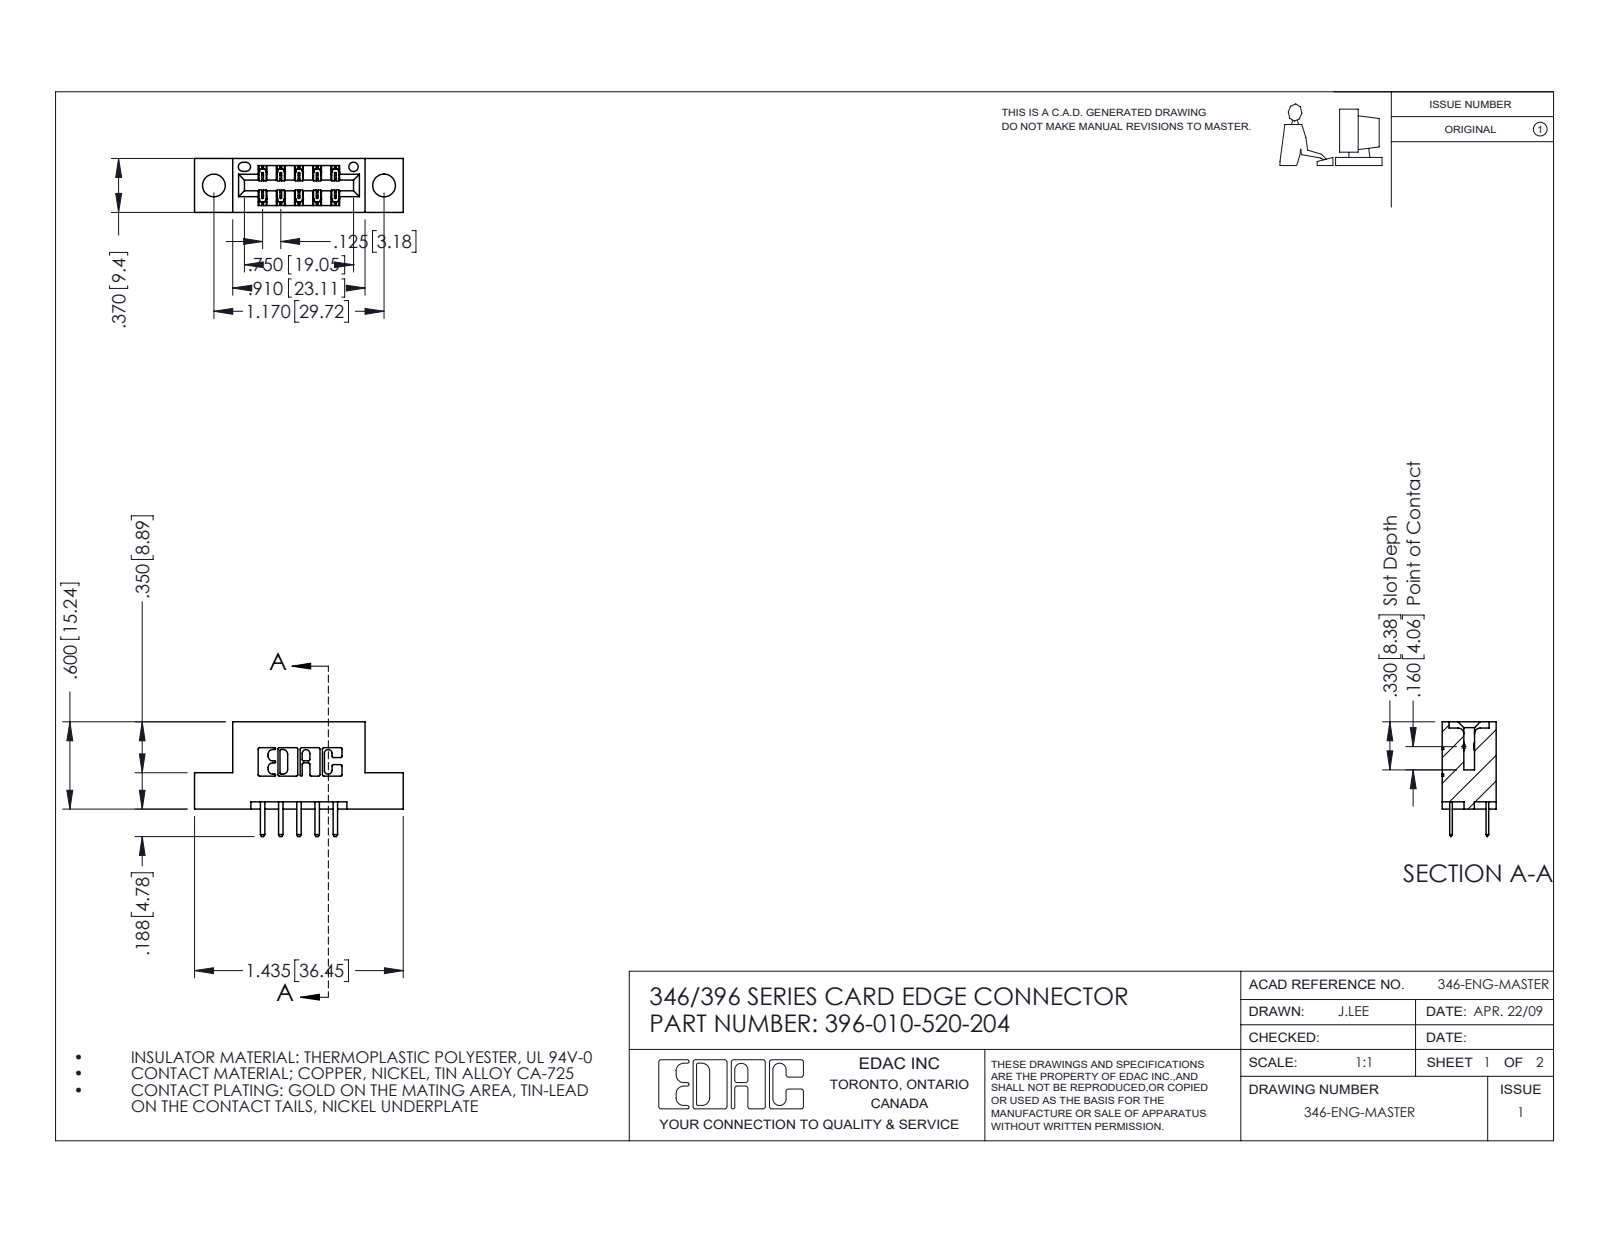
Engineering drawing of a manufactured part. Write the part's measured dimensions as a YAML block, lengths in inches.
part_name: "345-292-001_345-293-120; 346 Part_Flush Mounting Lugs - 0.156 Dia-TH; 396-010-520-204"
step_written_by: "SolidWorks 2016 (CONFIG_CONTROL_DESIGN)"
units: inches
bodies: {solids: 11, faces: 682, planar: 446, cylindrical: 236, other: 0}
overall_size: [1.435, 0.788, 0.37]
volume: 0.194
surface_area: 5.557
round_holes:
  - {diameter: 0.156, count: 2}
  - {diameter: 0.064, count: 1}
partial_cylinders:
  - {radius: 0.01, count: 22}
  - {radius: 0.006, count: 15}
  - {radius: 0.01, count: 14}
  - {radius: 0.007, count: 6}
  - {radius: 0.031, count: 6}
  - {radius: 0.026, count: 3}
  - {radius: 0.014, count: 2}
  - {radius: 0.022, count: 2}
face_to_face_distances: [0.25, 0.37, 0.048, 0.322, 0.148, 0.222, 0.1, 0.174, 0.125, 0.275]
hole_center_spacings: [0.246, 0.969, 1.17]
